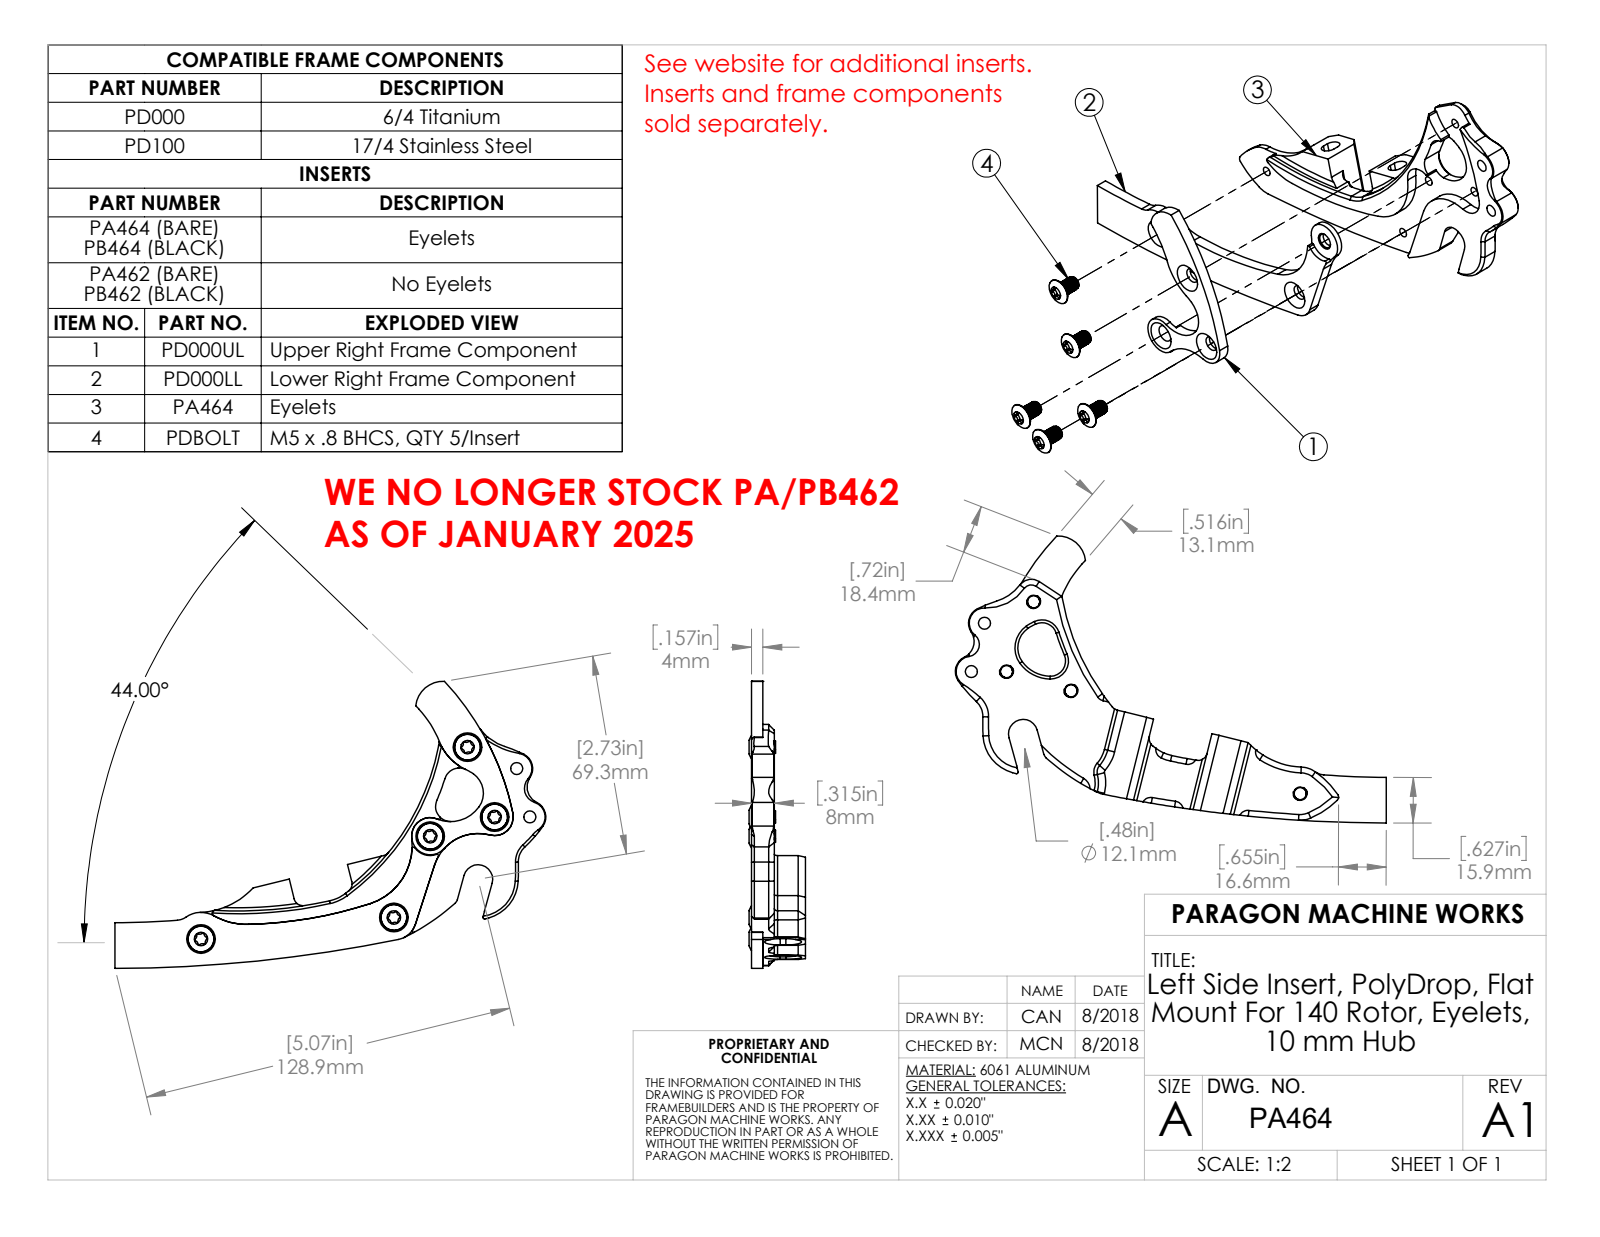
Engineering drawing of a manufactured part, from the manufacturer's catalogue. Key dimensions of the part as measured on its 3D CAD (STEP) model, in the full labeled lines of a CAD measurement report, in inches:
Part name (STEP PRODUCT): PA464
STEP written by: SolidWorks 2015 (AUTOMOTIVE_DESIGN)
Units: inches
Bodies: 1 solid, 201 faces (41 planar, 93 cylindrical, 67 other)
Overall size (bounding box): 5.271 × 3.313 × 0.741
Volume: 1.682 in³ · Surface area: 21.88 in²
Round holes (diameter × count): ⌀0.13 ×5, ⌀0.165 ×2
Partial cylindrical surfaces — rounded edges, fillets, slot ends (radius × count): R0.02 ×7, R0.045 ×5, R0.102 ×4, R0.217 ×4, R0.13 ×2, R0.22 ×2, R0.256 ×2, R0.5 ×2
Main face-to-face distances: 0.157, 0.315, 0.741, 0.584, 0.426, 1.339, 0.827, 0.512, 1.339, 0.949
Hole centre spacings: 0.484, 0.689, 0.732, 0.737, 0.924, 1.03, 1.223, 1.286
